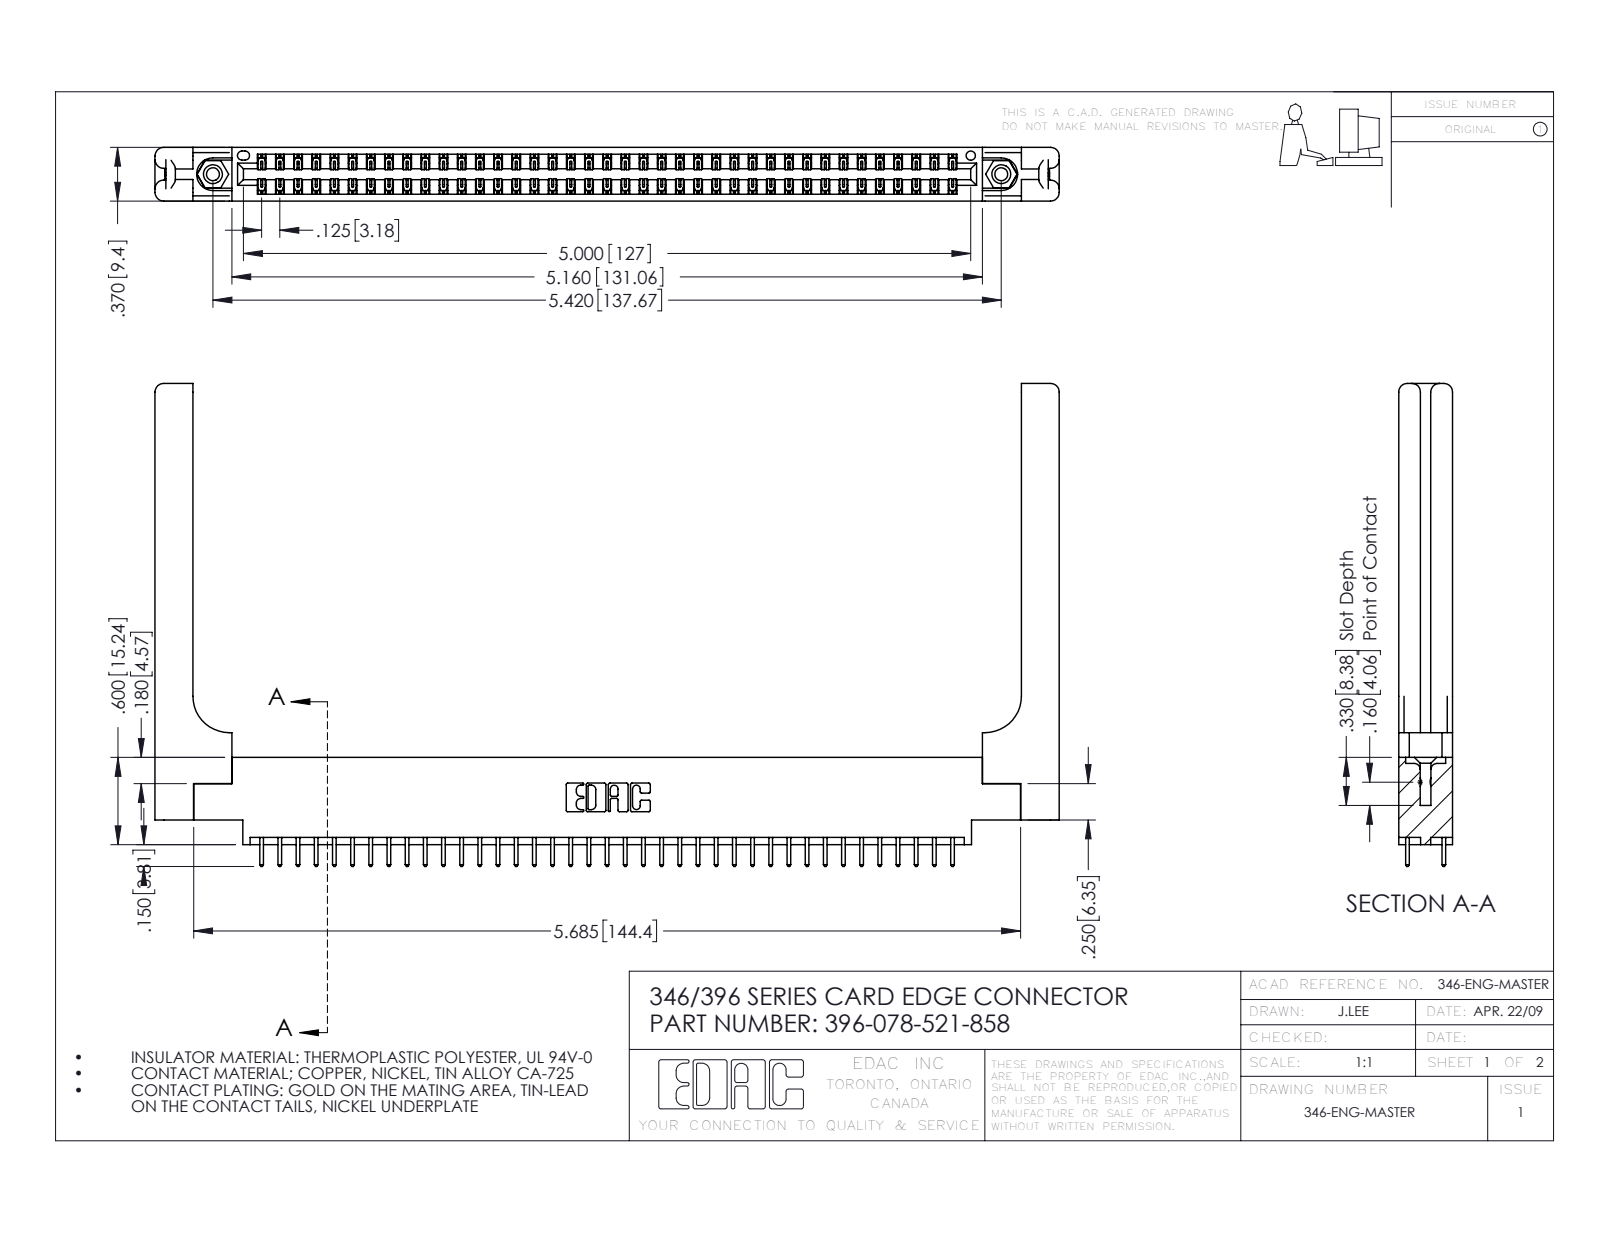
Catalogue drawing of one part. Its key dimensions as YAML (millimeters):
part_name: "345-250-001_345-250-001-102; 346 Part_0.170 Offset - 0.156 Dia-TH; 345-292-001_345-293-121; 346-220-058_345-220-058 (+1 more)"
step_written_by: "SolidWorks 2016 (CONFIG_CONTROL_DESIGN)"
units: millimeters
bodies: {solids: 83, faces: 4438, planar: 2958, cylindrical: 1420, other: 60}
overall_size: [157.9, 84.3, 9.4]
volume: 22680
surface_area: 25770
round_holes:
  - {diameter: 2.3, count: 2}
  - {diameter: 3.2, count: 2}
  - {diameter: 4, count: 2}
  - {diameter: 1.6, count: 1}
round_bosses_or_shafts:
  - {diameter: 3.9, count: 2}
partial_cylinders:
  - {radius: 0.2, count: 117}
  - {radius: 0.3, count: 78}
  - {radius: 0.3, count: 22}
  - {radius: 1.5, count: 16}
  - {radius: 0.2, count: 6}
  - {radius: 0.8, count: 6}
  - {radius: 0.7, count: 3}
  - {radius: 0.4, count: 2}
face_to_face_distances: [9.4, 1.2, 8.2, 1.8, 3.8, 3.8, 6.4, 0.6, 7.6, 7]
hole_center_spacings: [6.2, 132.4, 137.7]
